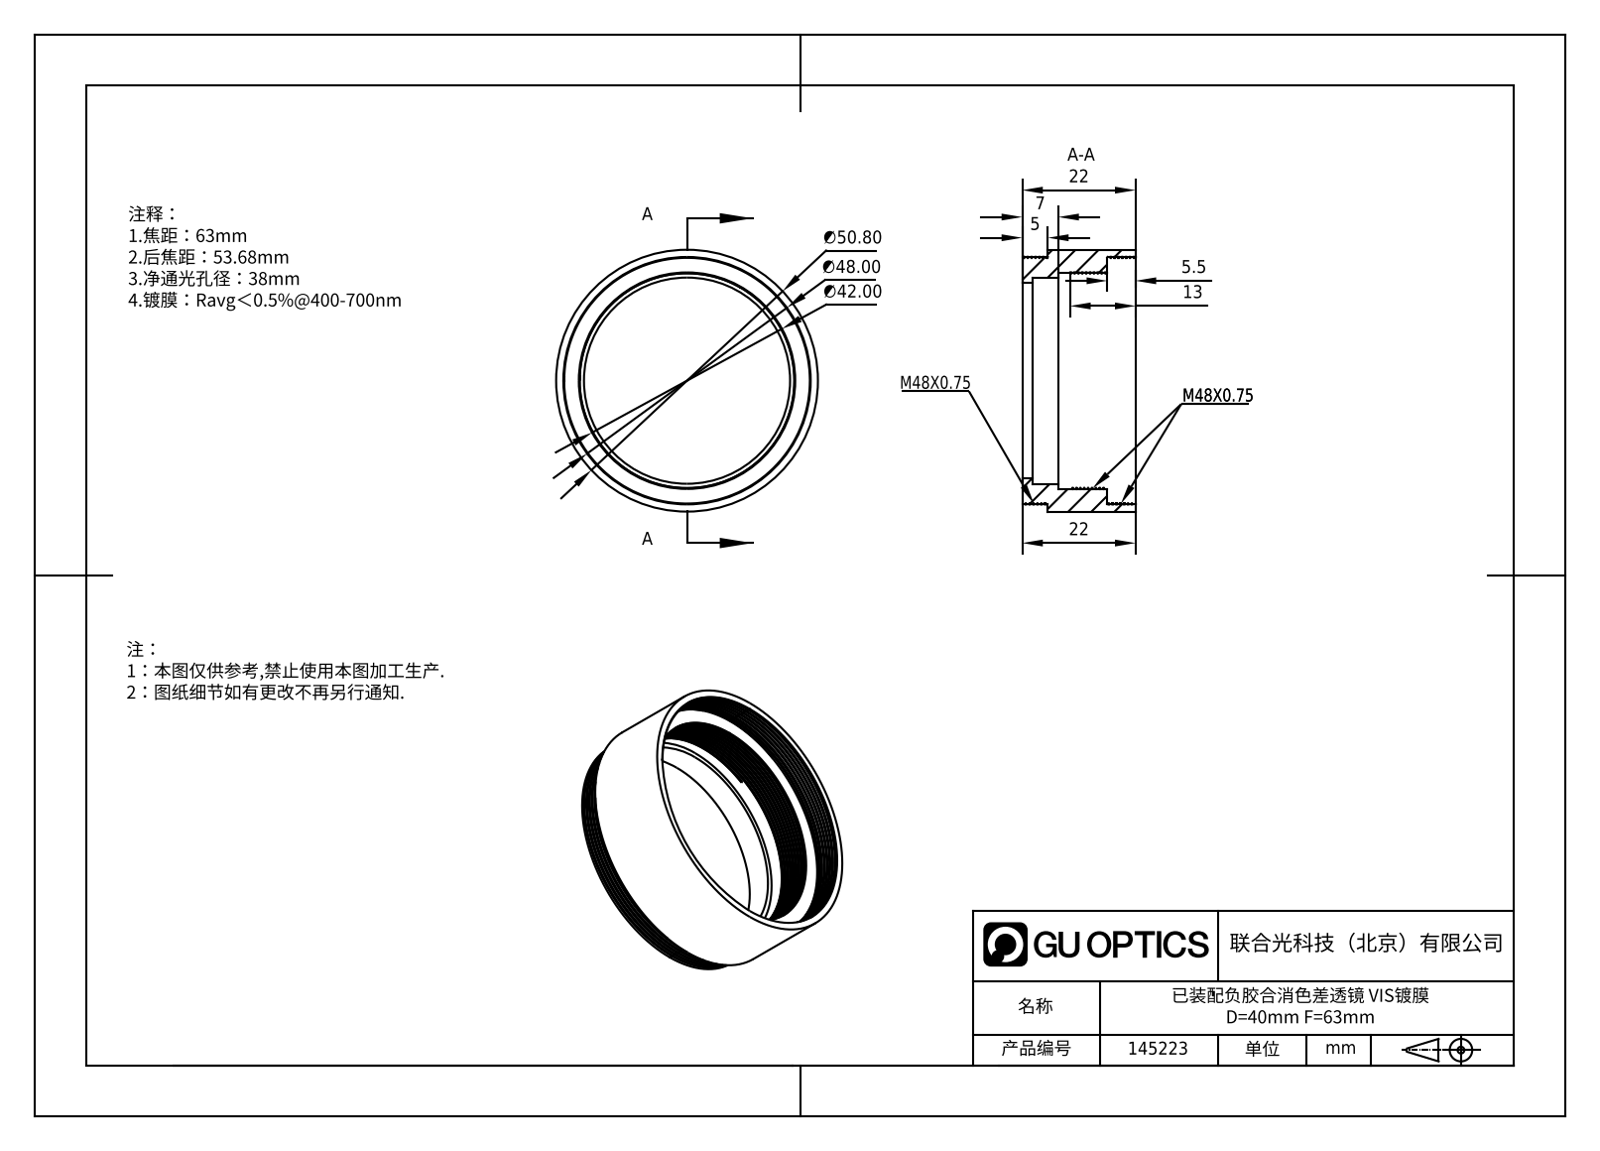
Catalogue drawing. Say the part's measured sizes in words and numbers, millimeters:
The part is named "APD-ML40-063-VIS-A". Its 3-D file was written by "SolidWorks 2023 (CONFIG_CONTROL_DESIGN)". It is 1 solid with 82 faces: 12 planar, 60 cylindrical and 10 other. Overall it measures 50.8 by 50.8 by 22 millimeters. Its volume is 11 884 cubic millimeters and its surface area 11 128 square millimeters. Round holes: 1 of diameter 38, 1 of diameter 40, 1 of diameter 42, 1 of diameter 48. Round bosses or shafts: 1 of diameter 50.8. The main face-to-face distances are 2, 2.01, 16.5, 14.5, 14.49, 5, 3, 2.99, 11.5, 22.
